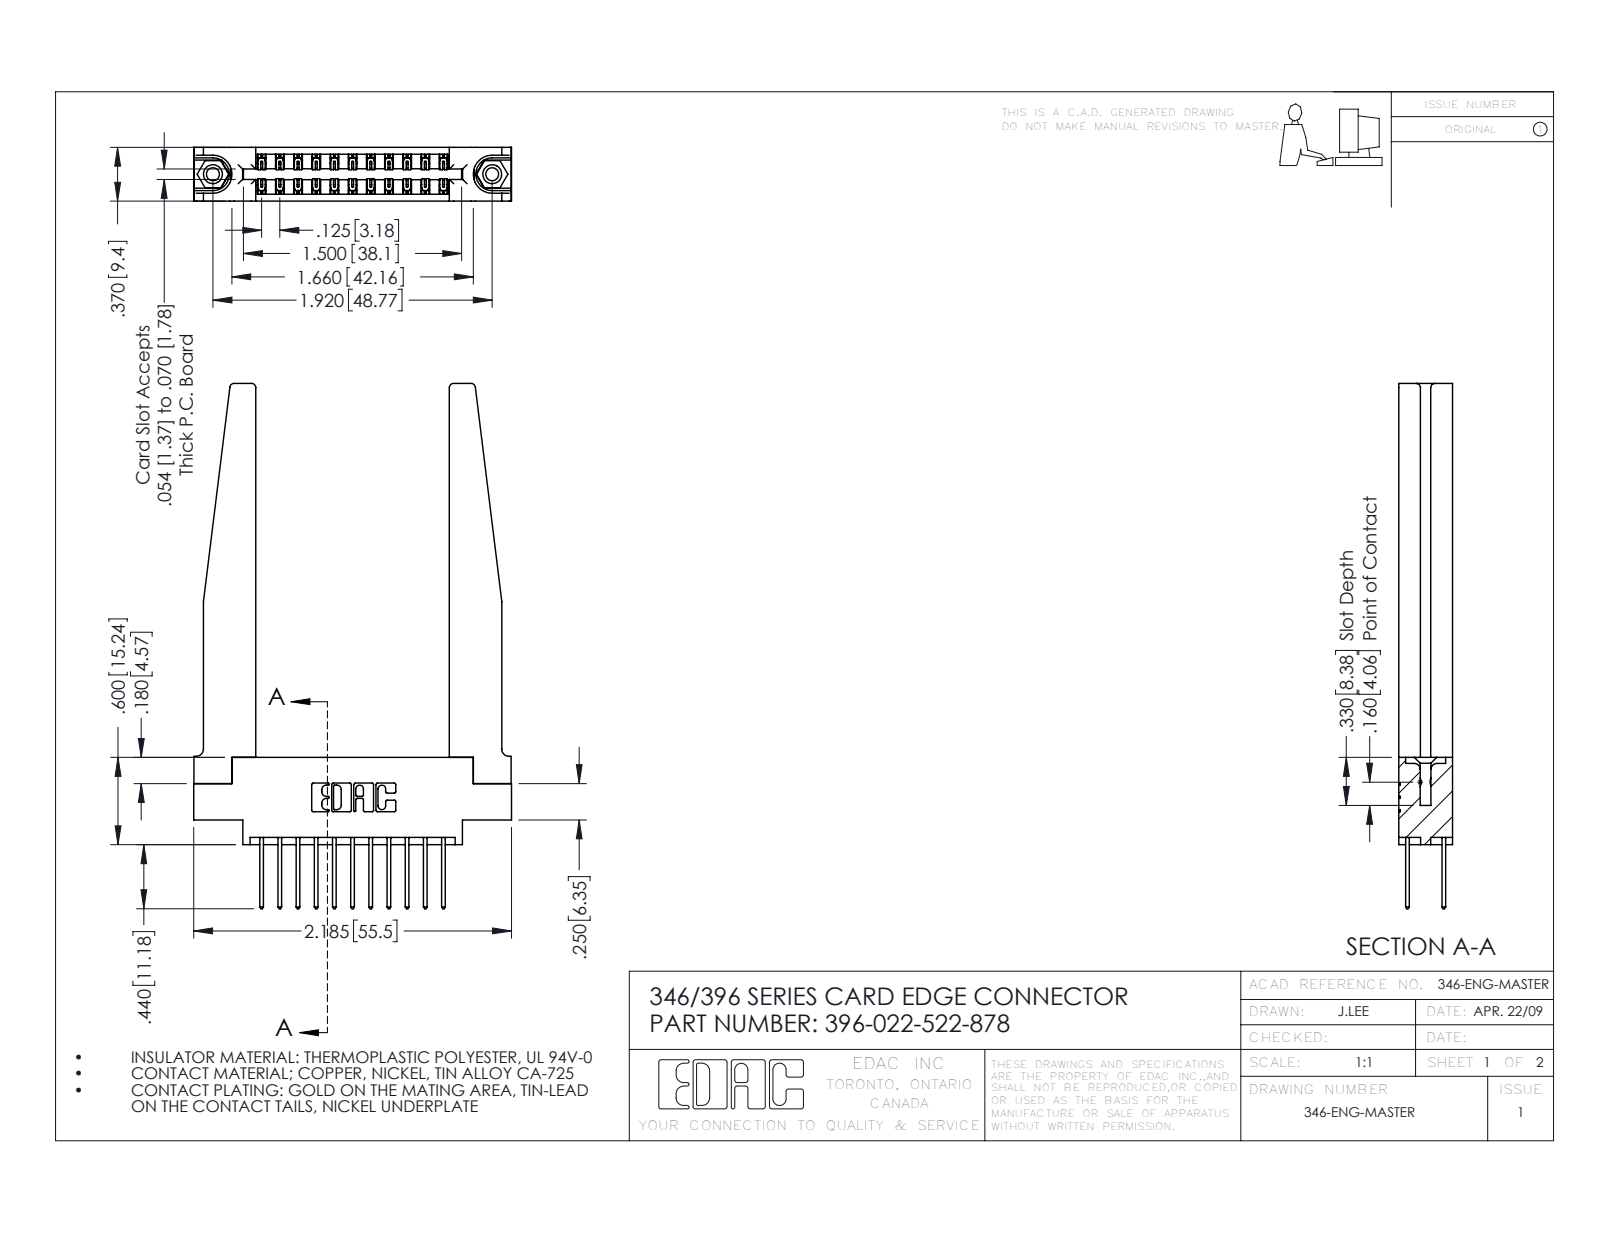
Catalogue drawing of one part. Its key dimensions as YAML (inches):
part_name: "346-220-078_345-220-078; 345-250-001_345-250-001-102; 345-292-001_345-293-122; 396-022-522-878 (+1 more)"
step_written_by: "SolidWorks 2016 (CONFIG_CONTROL_DESIGN)"
units: inches
bodies: {solids: 27, faces: 1504, planar: 992, cylindrical: 460, other: 52}
overall_size: [3.61, 2.185, 0.37]
volume: 0.731
surface_area: 20.87
round_holes:
  - {diameter: 0.089, count: 2}
  - {diameter: 0.125, count: 2}
  - {diameter: 0.156, count: 2}
  - {diameter: 0.064, count: 1}
round_bosses_or_shafts:
  - {diameter: 0.155, count: 2}
partial_cylinders:
  - {radius: 0.006, count: 33}
  - {radius: 0.01, count: 22}
  - {radius: 0.01, count: 22}
  - {radius: 0.03, count: 8}
  - {radius: 0.007, count: 6}
  - {radius: 0.031, count: 6}
  - {radius: 0.026, count: 3}
  - {radius: 0.014, count: 2}
face_to_face_distances: [0.37, 0.15, 0.072, 0.148, 0.048, 0.322, 0.25, 0.102, 0.22, 0.173]
hole_center_spacings: [0.246, 1.715, 1.92]
